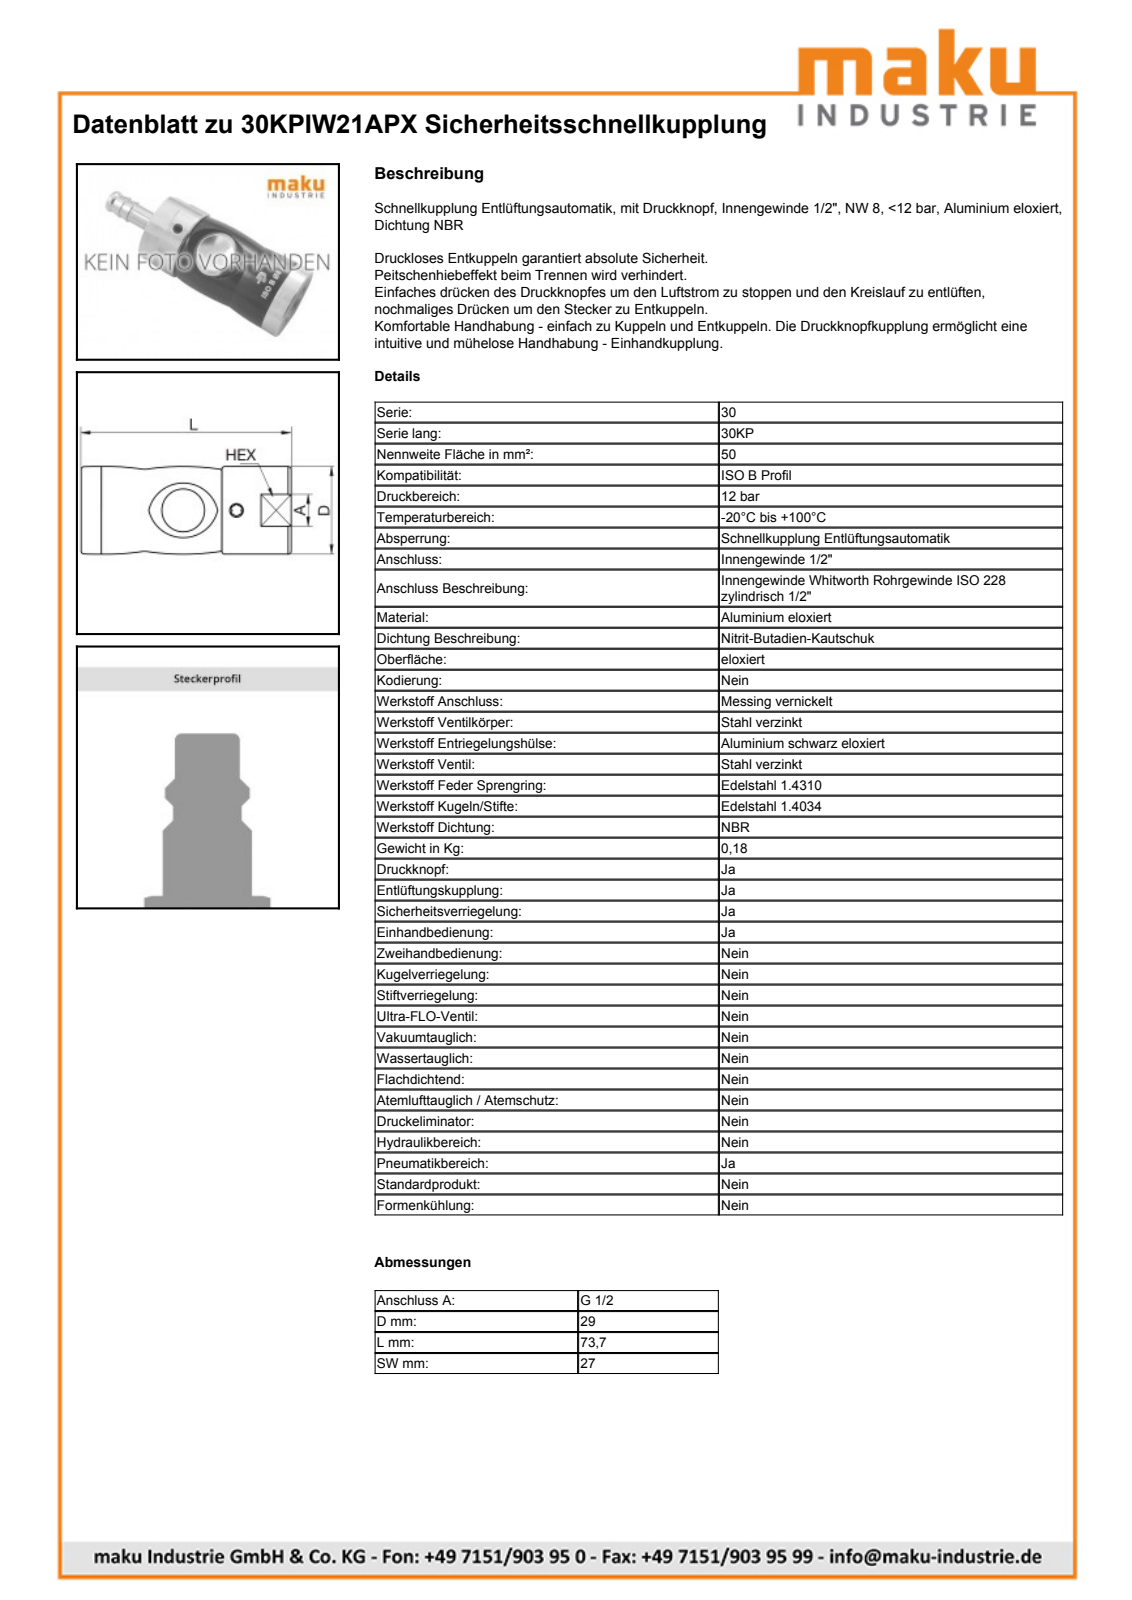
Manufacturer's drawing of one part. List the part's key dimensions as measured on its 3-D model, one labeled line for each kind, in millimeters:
Part name (STEP PRODUCT): 30KPIW21APX
STEP written by: Autodesk Inventor 2019 (CONFIG_CONTROL_DESIGN)
Units: millimetres
Bodies: 44 solids, 275 faces (80 planar, 88 cylindrical, 107 other)
Overall size (bounding box): 73.7 × 29.04 × 29.04
Volume: 49 230 mm³ · Surface area: 30 083 mm²
Round holes (diameter × count): ⌀3.5 ×1, ⌀8 ×1, ⌀8.5 ×1, ⌀11.1 ×1, ⌀11.2 ×1, ⌀12.2 ×1, ⌀13.6 ×1, ⌀14 ×1, ⌀16 ×1, ⌀17.5 ×1, ⌀18.1 ×1, ⌀18.6 ×1
Round bosses / shafts (diameter × count): ⌀29.01 ×1, ⌀26 ×1, ⌀24.5 ×1, ⌀24.31 ×1, ⌀20.5 ×1, ⌀19.15 ×1, ⌀18.2 ×1, ⌀18 ×1
Partial cylindrical surfaces — rounded edges, fillets, slot ends (radius × count): R2.5 ×4, R7.1 ×2, R5.2 ×1
Main face-to-face distances: 46.7, 6.7, 40, 11.58, 51.58, 58.28, 10, 55.8, 15.42, 27
Hole centre spacings: 17.65
